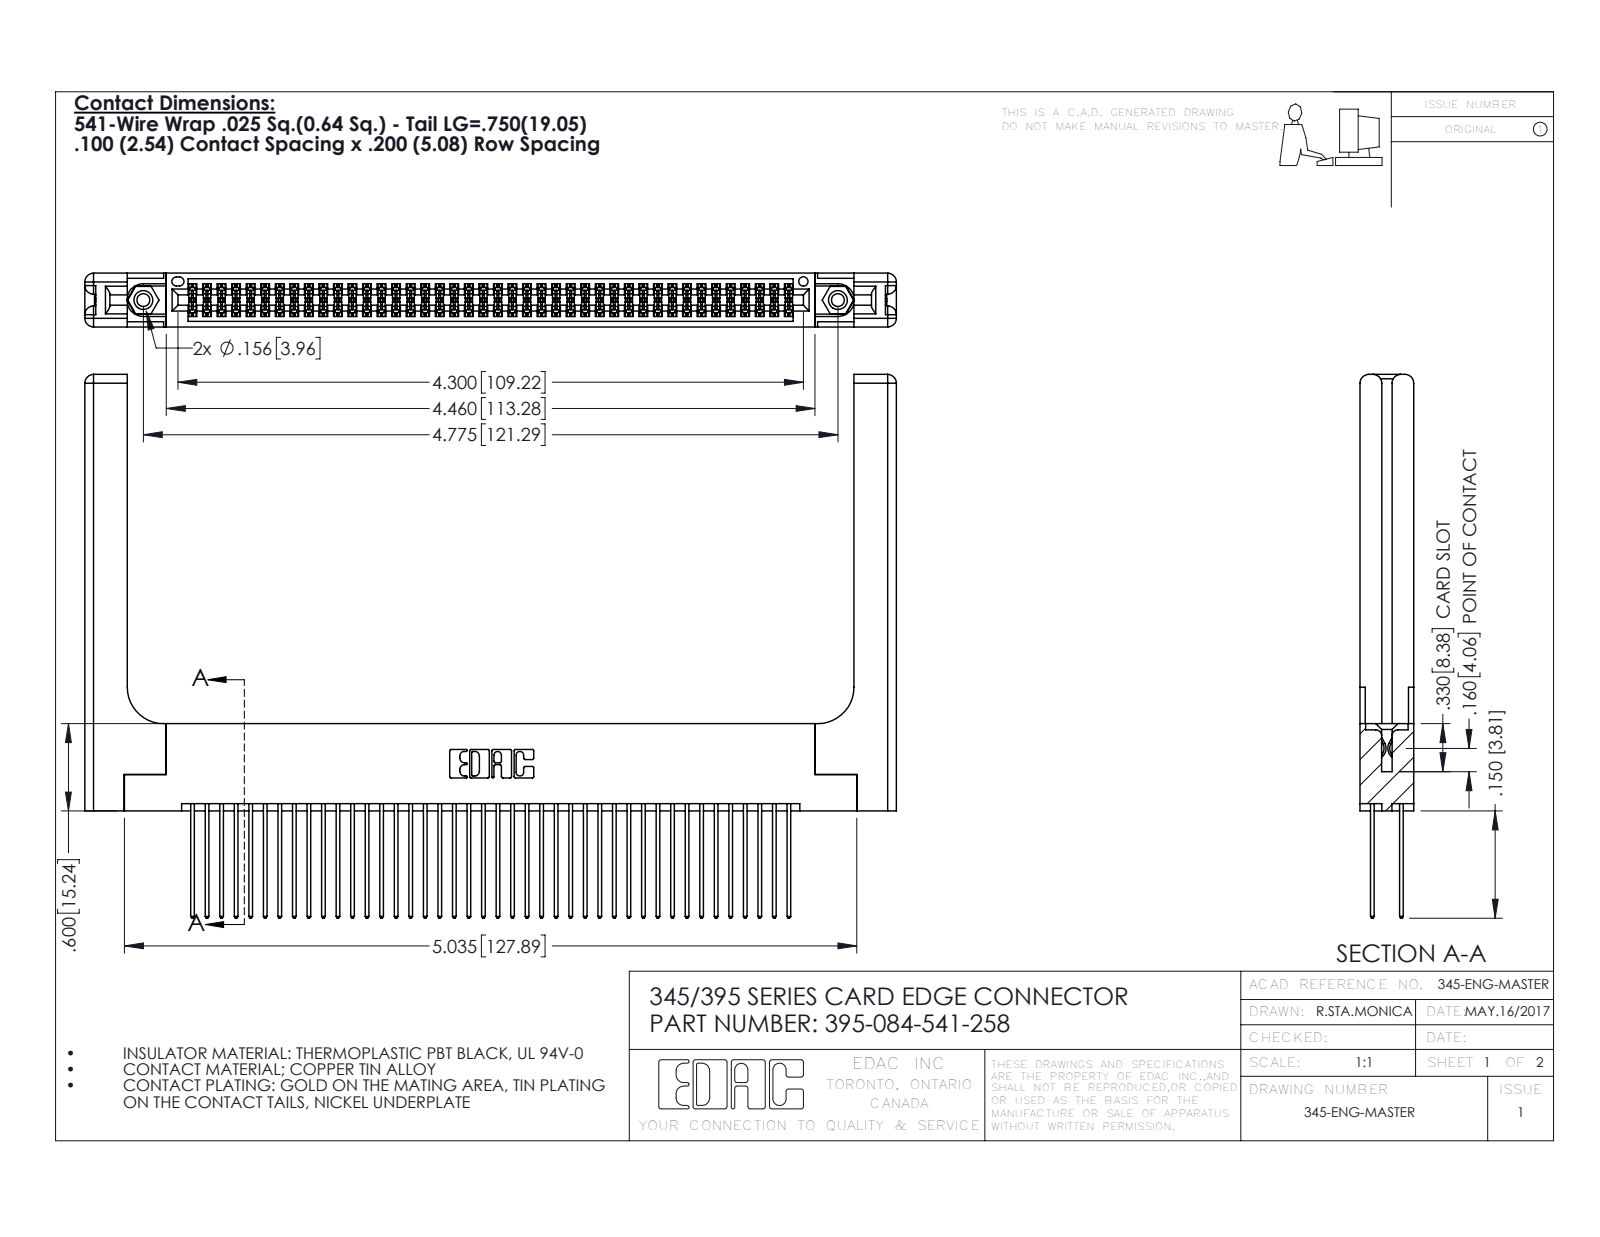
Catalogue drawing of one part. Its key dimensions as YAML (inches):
part_name: "345-220-058_345-220-058; 345-292-001_345-293-141; 395-084-541-258; 345-250-001_345-250-001-102 (+1 more)"
step_written_by: "SolidWorks 2016 (CONFIG_CONTROL_DESIGN)"
units: inches
bodies: {solids: 89, faces: 4582, planar: 3000, cylindrical: 1522, other: 60}
overall_size: [5.579, 3.737, 0.37]
volume: 1.387
surface_area: 44
round_holes:
  - {diameter: 0.089, count: 2}
  - {diameter: 0.125, count: 2}
  - {diameter: 0.156, count: 2}
  - {diameter: 0.064, count: 1}
round_bosses_or_shafts:
  - {diameter: 0.155, count: 2}
partial_cylinders:
  - {radius: 0.006, count: 126}
  - {radius: 0.01, count: 84}
  - {radius: 0.01, count: 22}
  - {radius: 0.06, count: 16}
  - {radius: 0.007, count: 6}
  - {radius: 0.031, count: 6}
  - {radius: 0.026, count: 3}
  - {radius: 0.014, count: 2}
face_to_face_distances: [0.072, 0.298, 0.37, 0.2, 0.098, 0.272, 0.025, 0.225, 0.175, 0.148]
hole_center_spacings: [0.27, 4.539, 4.775]
